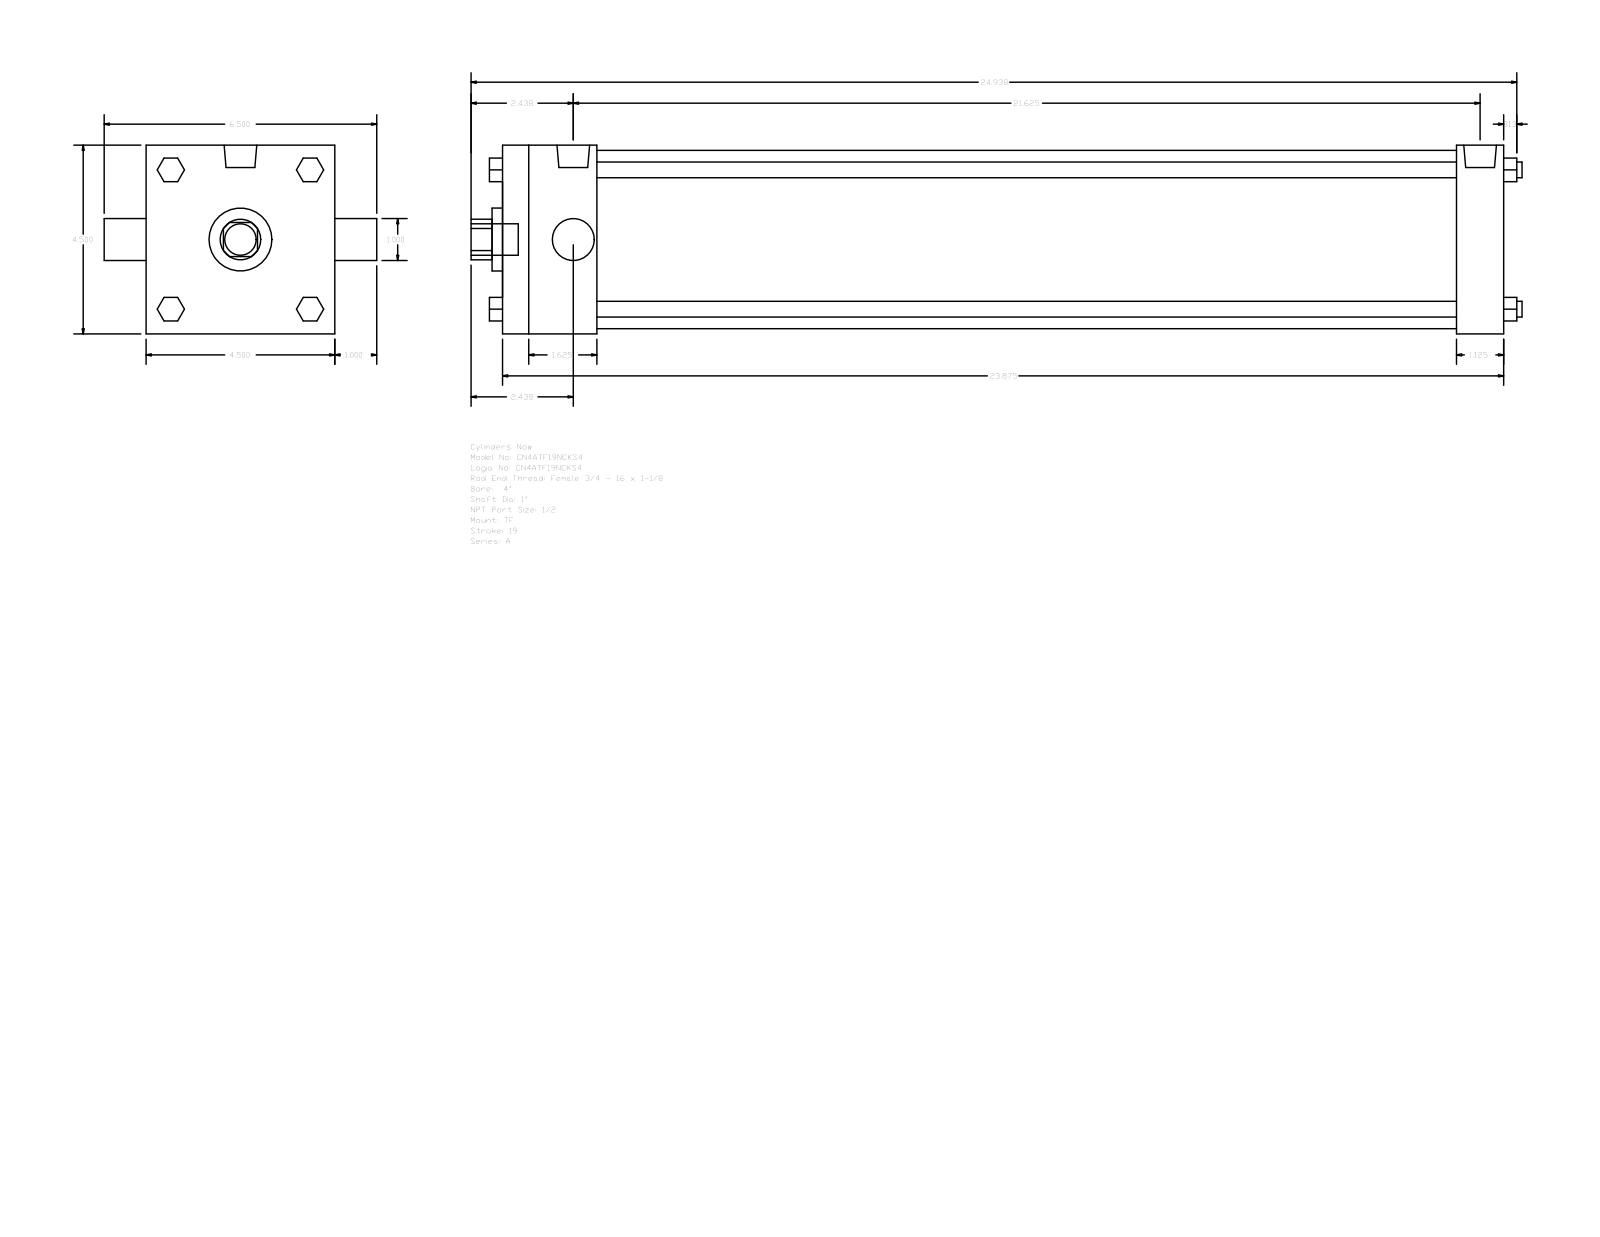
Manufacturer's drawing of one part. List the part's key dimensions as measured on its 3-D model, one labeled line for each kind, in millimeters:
Part name (STEP PRODUCT): A_TF__0400_1
STEP written by: GSSL Pune (CONFIG_CONTROL_DESIGN)
Units: millimetres
Bodies: 0 solids, 120 faces (92 planar, 28 cylindrical, 0 other)
Overall size (bounding box): 636.59 × 165.1 × 114.3
Round holes (diameter × count): ⌀25.4 ×2, ⌀38.1 ×1, ⌀107.95 ×1
Round bosses / shafts (diameter × count): ⌀9.53 ×4, ⌀8.73 ×3, ⌀19.77 ×2, ⌀19.05 ×1
Partial cylindrical surfaces — rounded edges, fillets, slot ends (radius × count): R12.29 ×1
Main face-to-face distances: 114.3, 606.43, 577.85, 28.58, 57.15, 520.7, 549.28, 14.29, 42.16, 73.03
